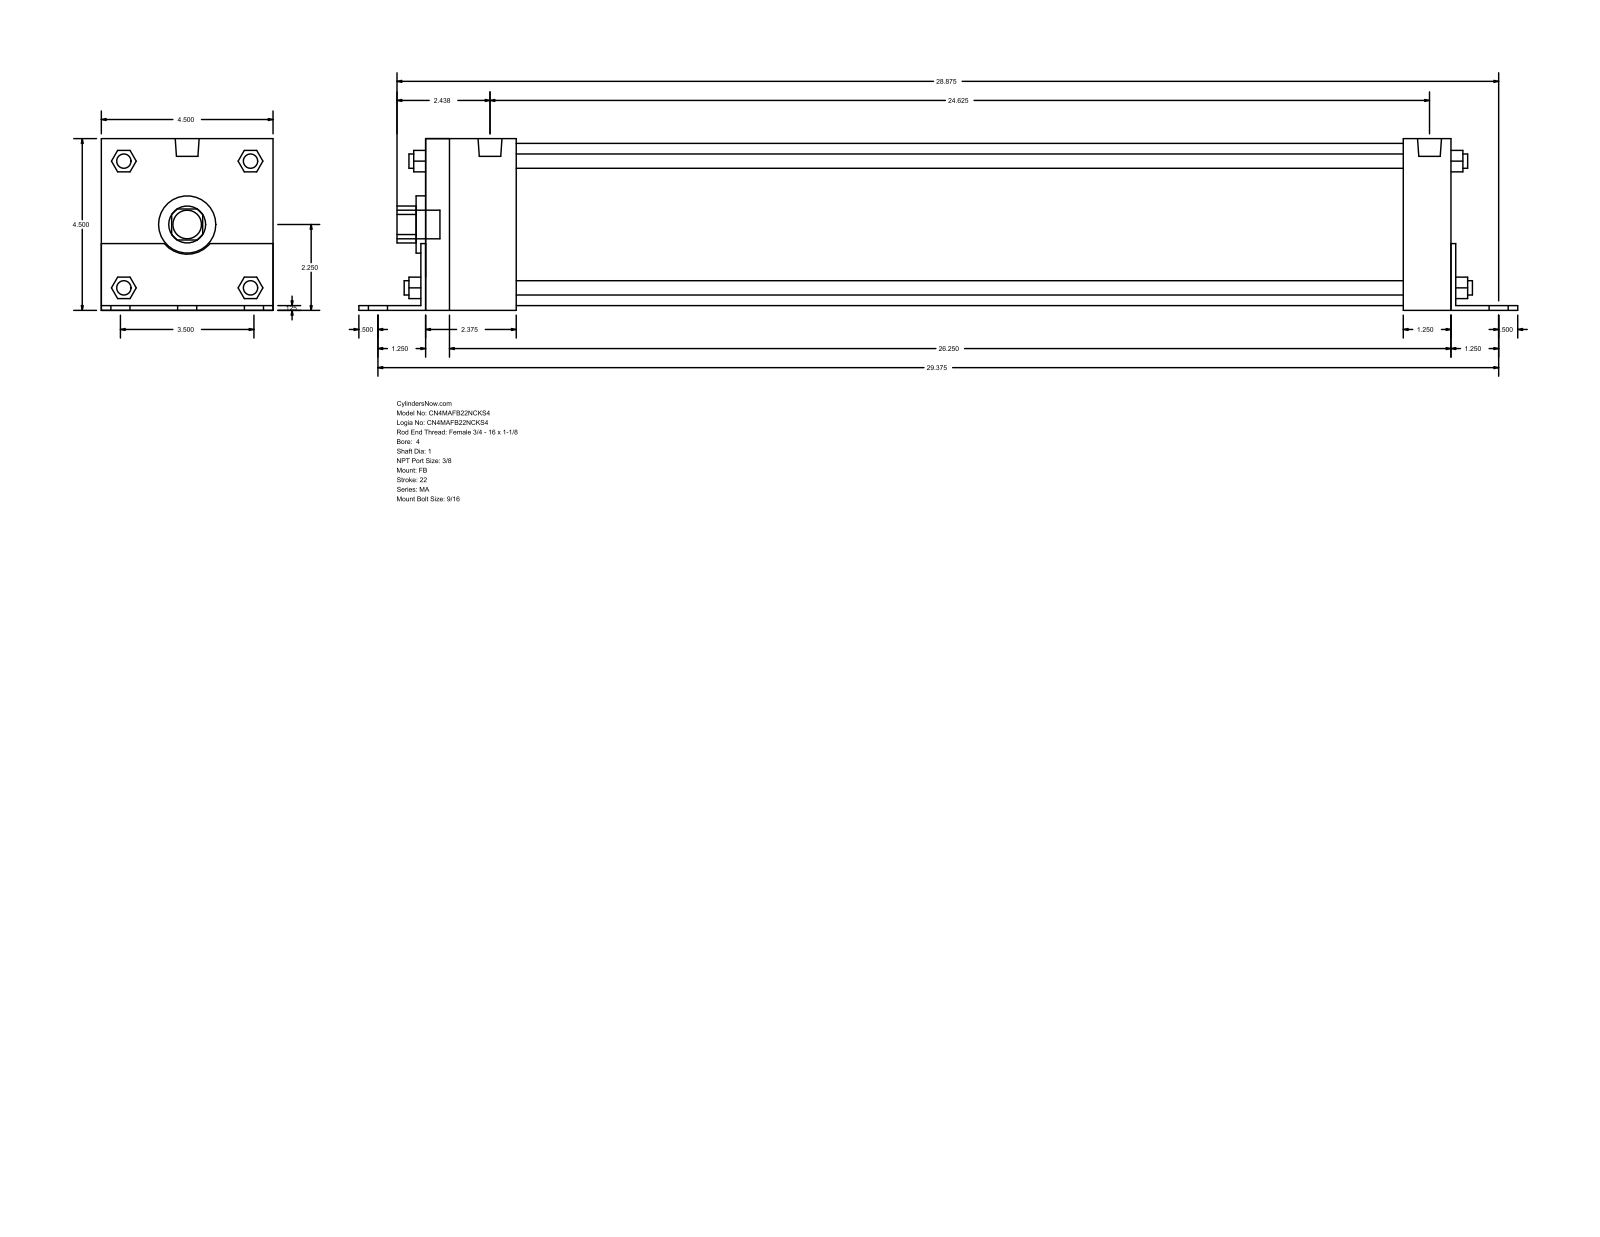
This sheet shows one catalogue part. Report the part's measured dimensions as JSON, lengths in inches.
{"part_name": "MA_FB__0400_1", "step_written_by": "GSSL Pune (CONFIG_CONTROL_DESIGN)", "units": "inches", "bodies": {"solids": 0, "faces": 140, "planar": 105, "cylindrical": 35, "other": 0}, "overall_size": [30.375, 4.502, 4.5], "round_holes": [[1, 1], [1.5, 1], [4.25, 1]], "round_bosses_or_shafts": [[0.563, 6], [0.437, 4], [0.375, 4], [0.627, 2], [0.75, 1]], "partial_cylinders_radius": [[0.484, 1], [0.78, 1]], "face_to_face_distances": [4.5, 0.125, 4.502, 0.123, 4.377, 26.875, 0.125, 27.125, 27, 27]}
